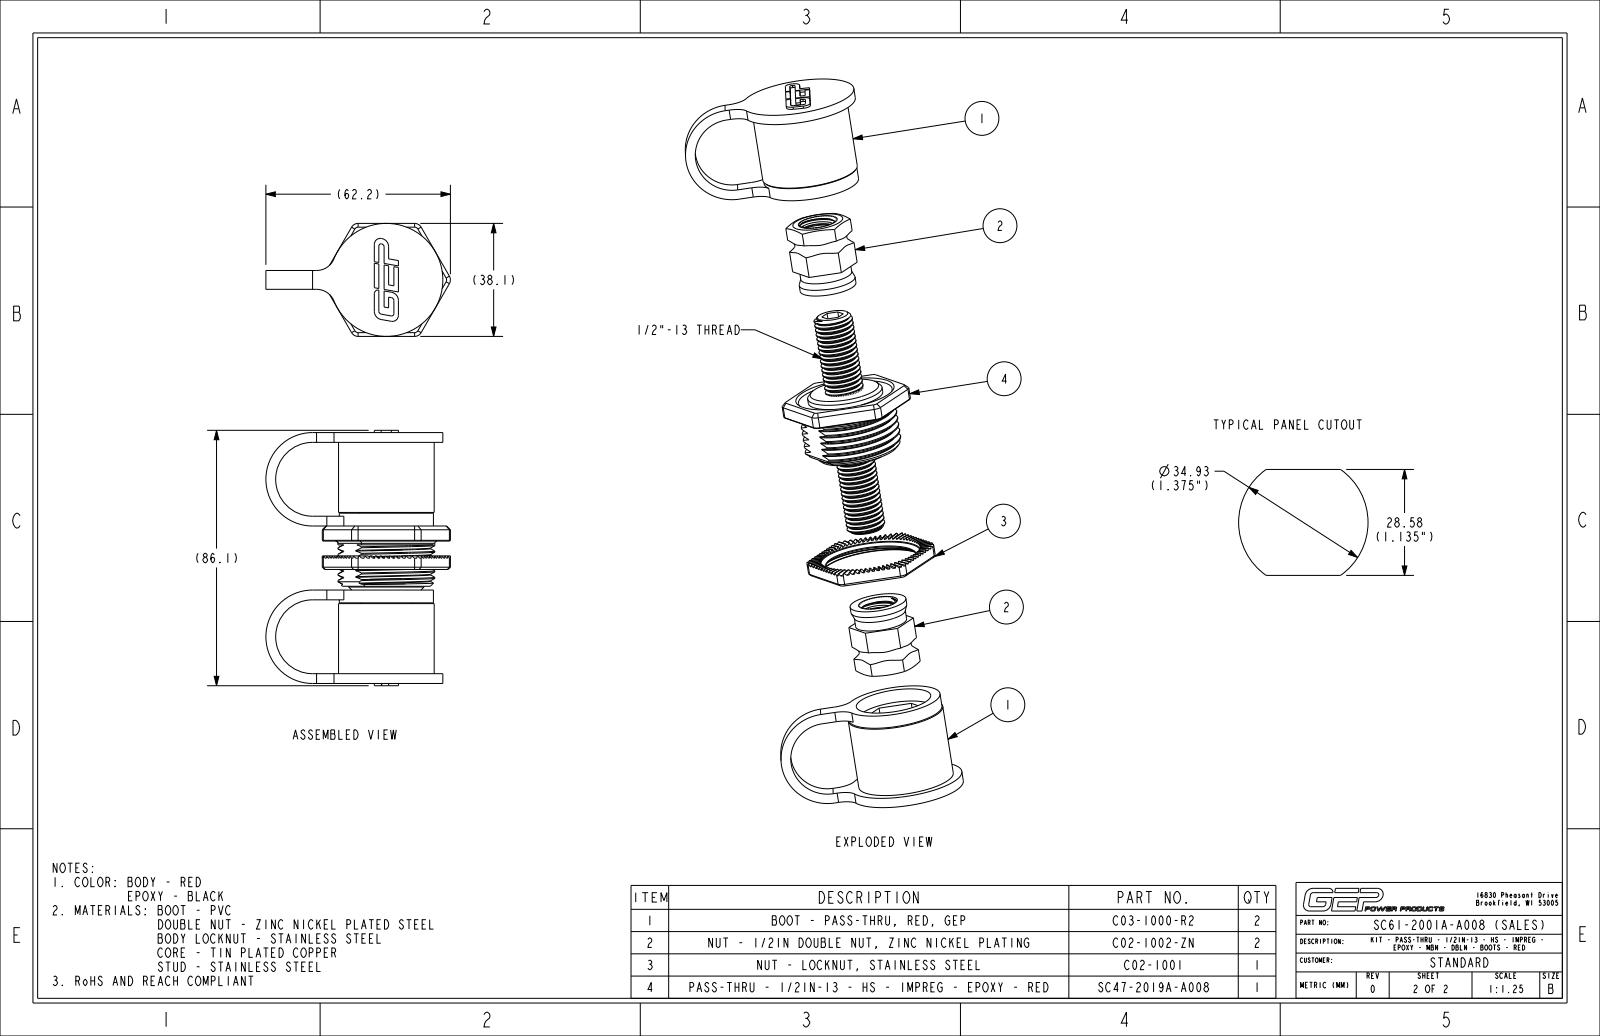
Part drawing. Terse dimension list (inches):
name: C07-1002_NCF; PC40-2005A-B008_MOLD_NCF; PC40-2005A-B008_NCF_ASM; PC05-2016A-A000_NCF (+8 more)
written by: CREO PARAMETRIC BY PTC INC, 2024014 (CONFIG_CONTROL_DESIGN)
unit: in
bodies: 10 solids, 1290 faces (742 planar, 289 cylindrical, 259 other)
size: 3.39 × 2.198 × 1.759
volume: 4.321 in³; area: 68.19 in²
holes: 1× ⌀0.422, 1× ⌀0.84, 1× ⌀1, 1× ⌀1.26, 1× ⌀1.347
bosses: 1× ⌀1.5, 1× ⌀1.27, 1× ⌀1.26, 1× ⌀1.25, 1× ⌀0.75, 1× ⌀0.685, 1× ⌀0.51
rounds: 6× R0.03, 6× R0.04, 6× R0.1, 6× R0.11, 6× R0.181, 4× R0.08, 4× R0.25, 2× R0.05
face distances: 0.75, 1.24, 2.09, 0.13, 3.2, 0.25, 1.11, 1.96, 3.33, 0.17
